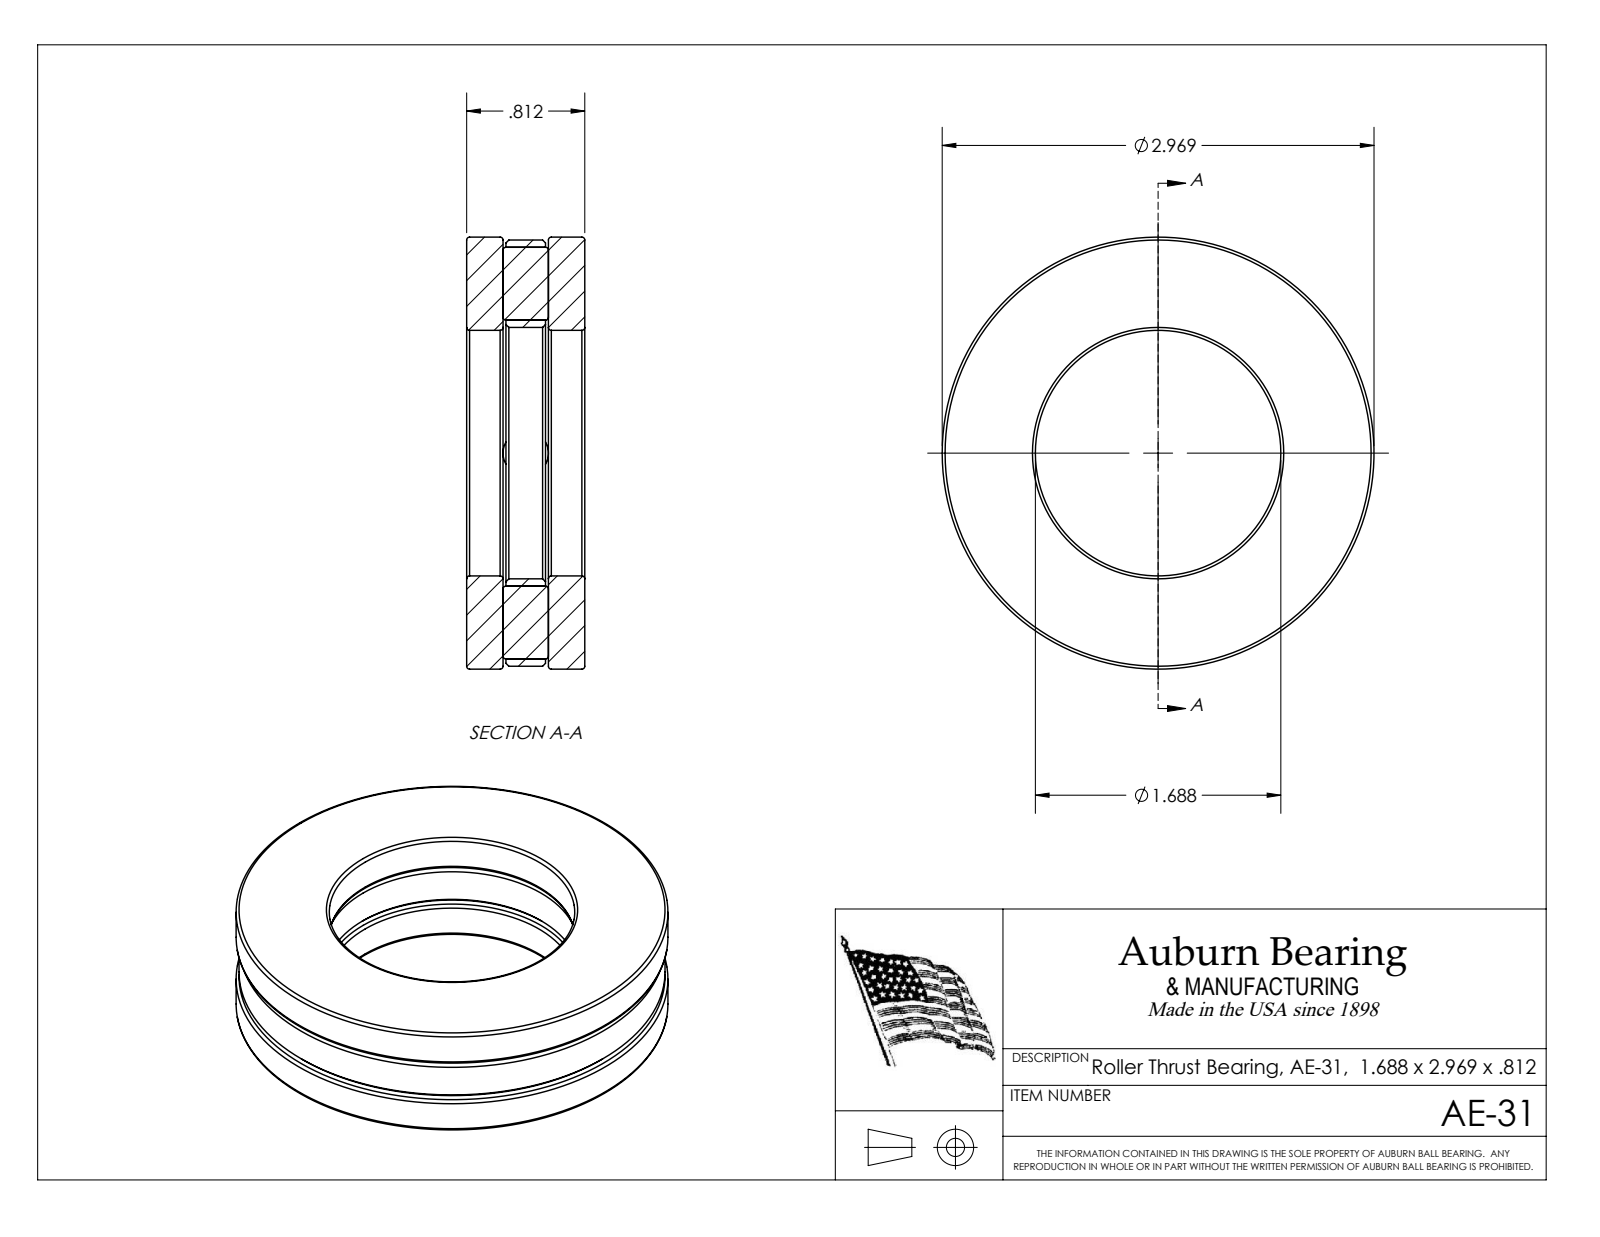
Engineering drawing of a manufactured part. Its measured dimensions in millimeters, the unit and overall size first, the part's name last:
Units: millimetres
Overall size (bounding box): 75.4 × 75.4 × 20.6
Round holes (diameter × count): ⌀42.8 ×1, ⌀43.9 ×1
Round bosses / shafts (diameter × count): ⌀7.9 ×2, ⌀75.4 ×1, ⌀74.4 ×1
Main face-to-face distances: 6.4, 14.3, 6.9, 13.8, 0.5, 7.4, 7.9, 20.6, 6.9, 19.3
Volume: 57 500 mm³ · Surface area: 26 450 mm²
Bodies: 7 solids, 60 faces (30 planar, 10 cylindrical, 20 other)
Part name (STEP PRODUCT): AE-31
STEP written by: SolidWorks 2017 (CONFIG_CONTROL_DESIGN)
